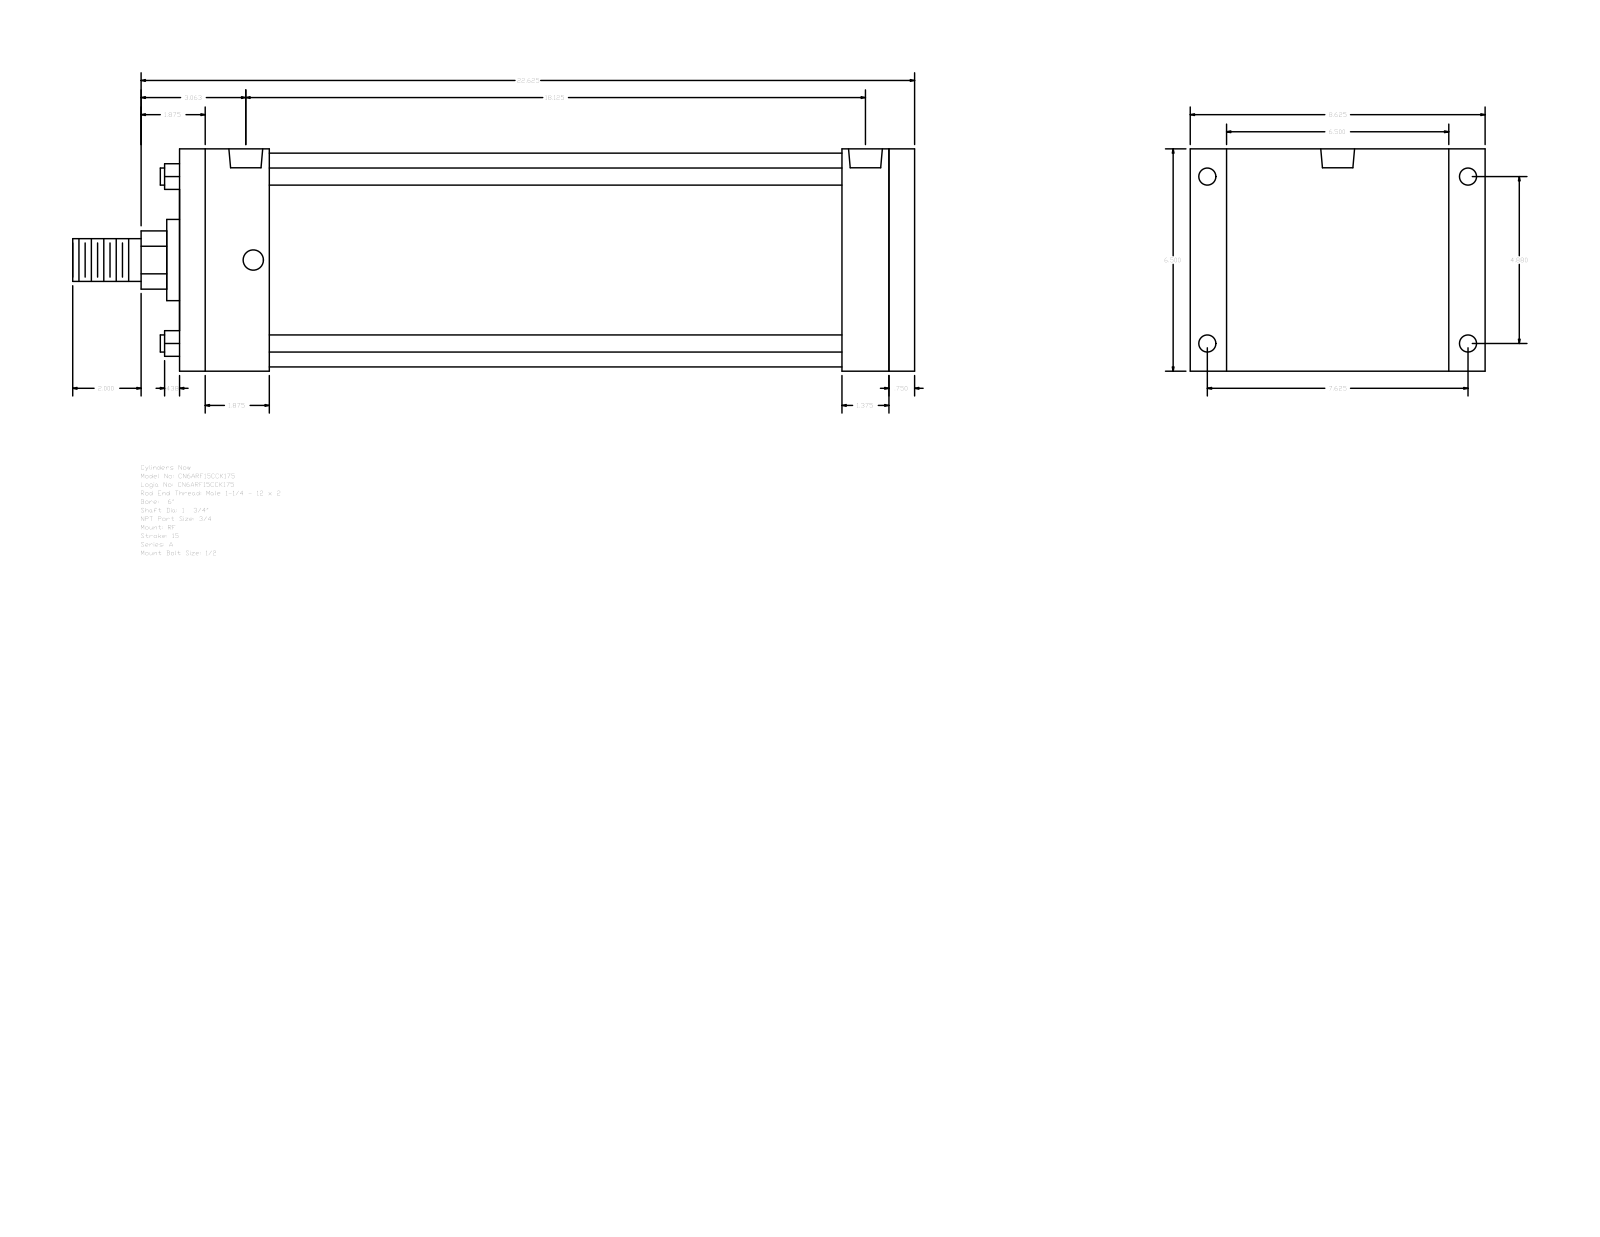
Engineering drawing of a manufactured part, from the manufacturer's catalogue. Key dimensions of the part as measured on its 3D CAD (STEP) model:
Part name (STEP PRODUCT): A_RF__0600_1.75
STEP written by: GSSL Pune (CONFIG_CONTROL_DESIGN)
Units: millimetres
Bodies: 0 solids, 92 faces (64 planar, 28 cylindrical, 0 other)
Overall size (bounding box): 625.48 × 219.07 × 165.1
Round holes (diameter × count): ⌀12.7 ×4, ⌀15.08 ×4, ⌀25.12 ×2
Round bosses / shafts (diameter × count): ⌀12.7 ×4, ⌀158.75 ×1, ⌀60.33 ×1, ⌀44.45 ×1, ⌀31.75 ×1
Partial cylindrical surfaces — rounded edges, fillets, slot ends (radius × count): R21.63 ×1
Main face-to-face distances: 165.1, 546.1, 19.05, 527.05, 66.68, 460.37, 479.42, 492.13, 425.45, 34.92
Hole centre spacings: 5.56, 123.96, 193.68, 229.95, 449.25, 454.81, 460.37
